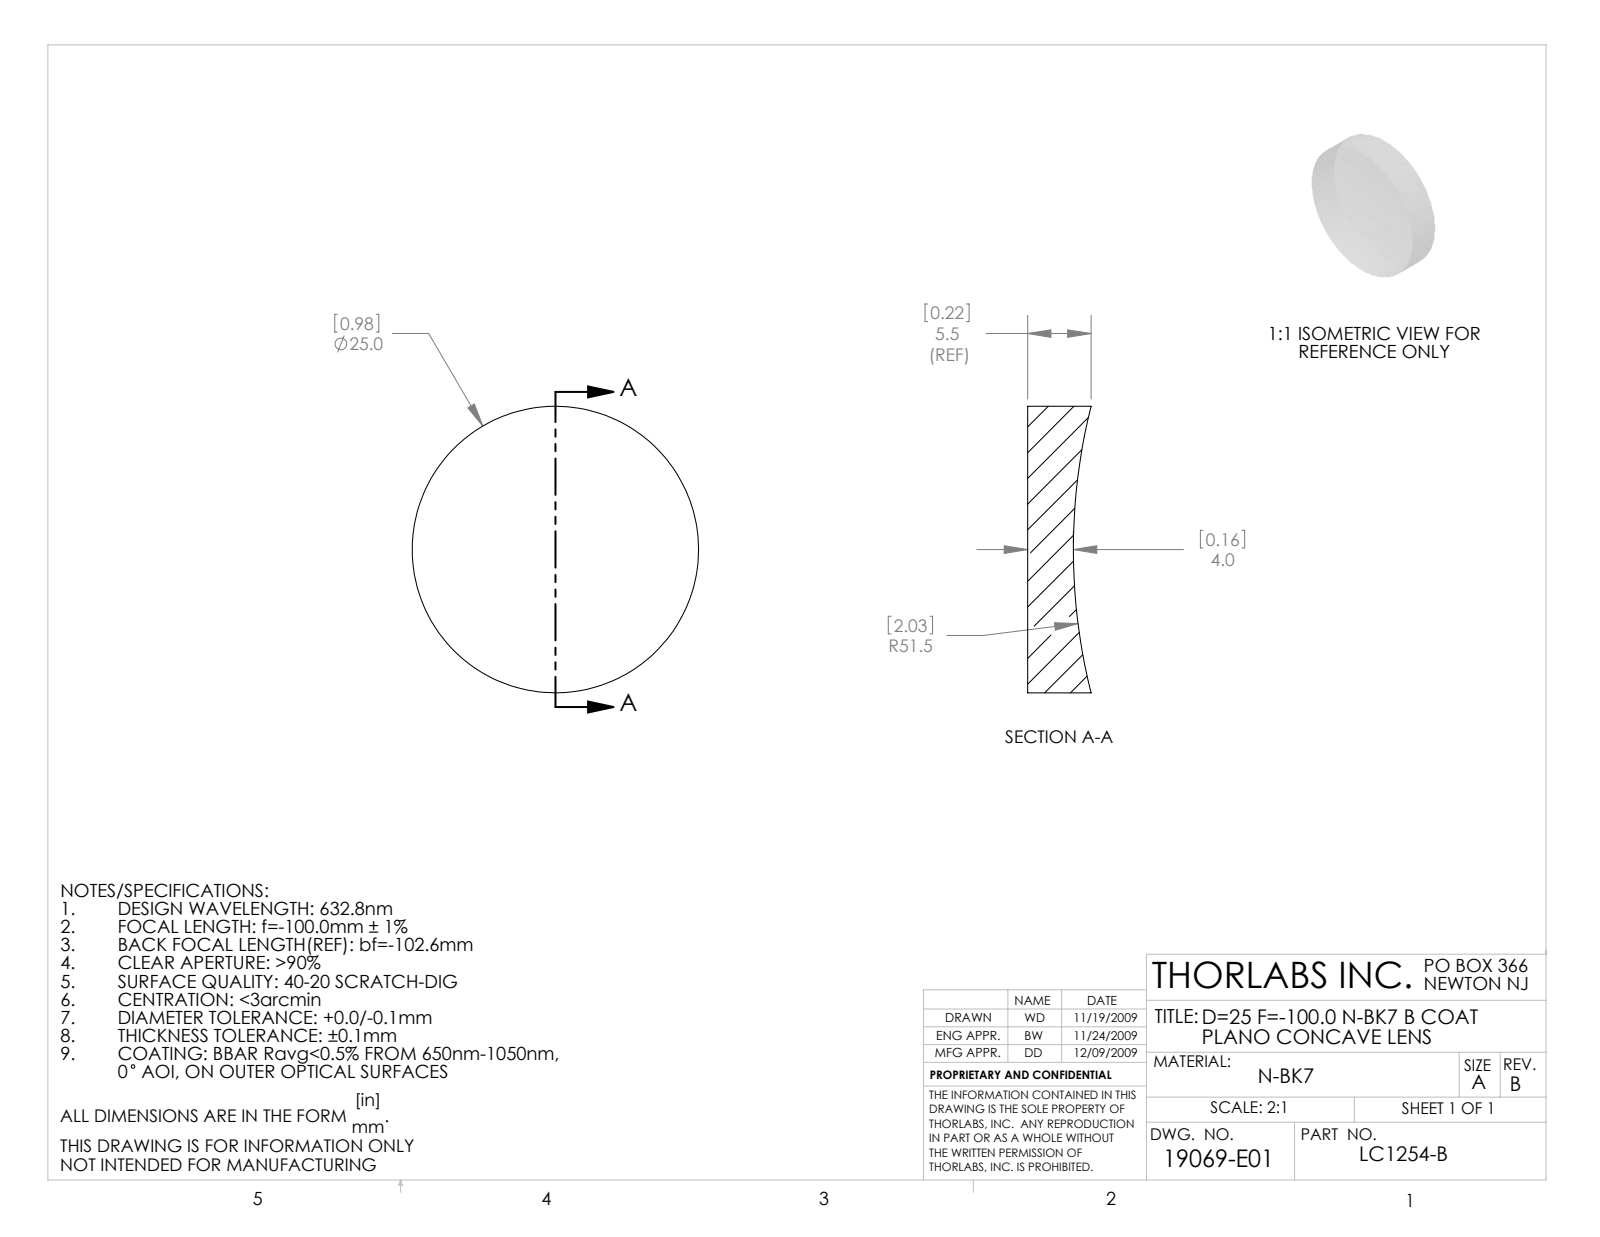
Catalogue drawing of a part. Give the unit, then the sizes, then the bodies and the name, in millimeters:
Units: millimetres
Overall size (bounding box): 25 × 25 × 5.54
Round bosses / shafts (diameter × count): ⌀25 ×1
Volume: 2 340 mm³ · Surface area: 1 424 mm²
Bodies: 1 solid, 5 faces (1 planar, 2 cylindrical, 2 other)
Part name (STEP PRODUCT): 19069-E0W
STEP written by: SolidWorks 2009 (AUTOMOTIVE_DESIGN)
